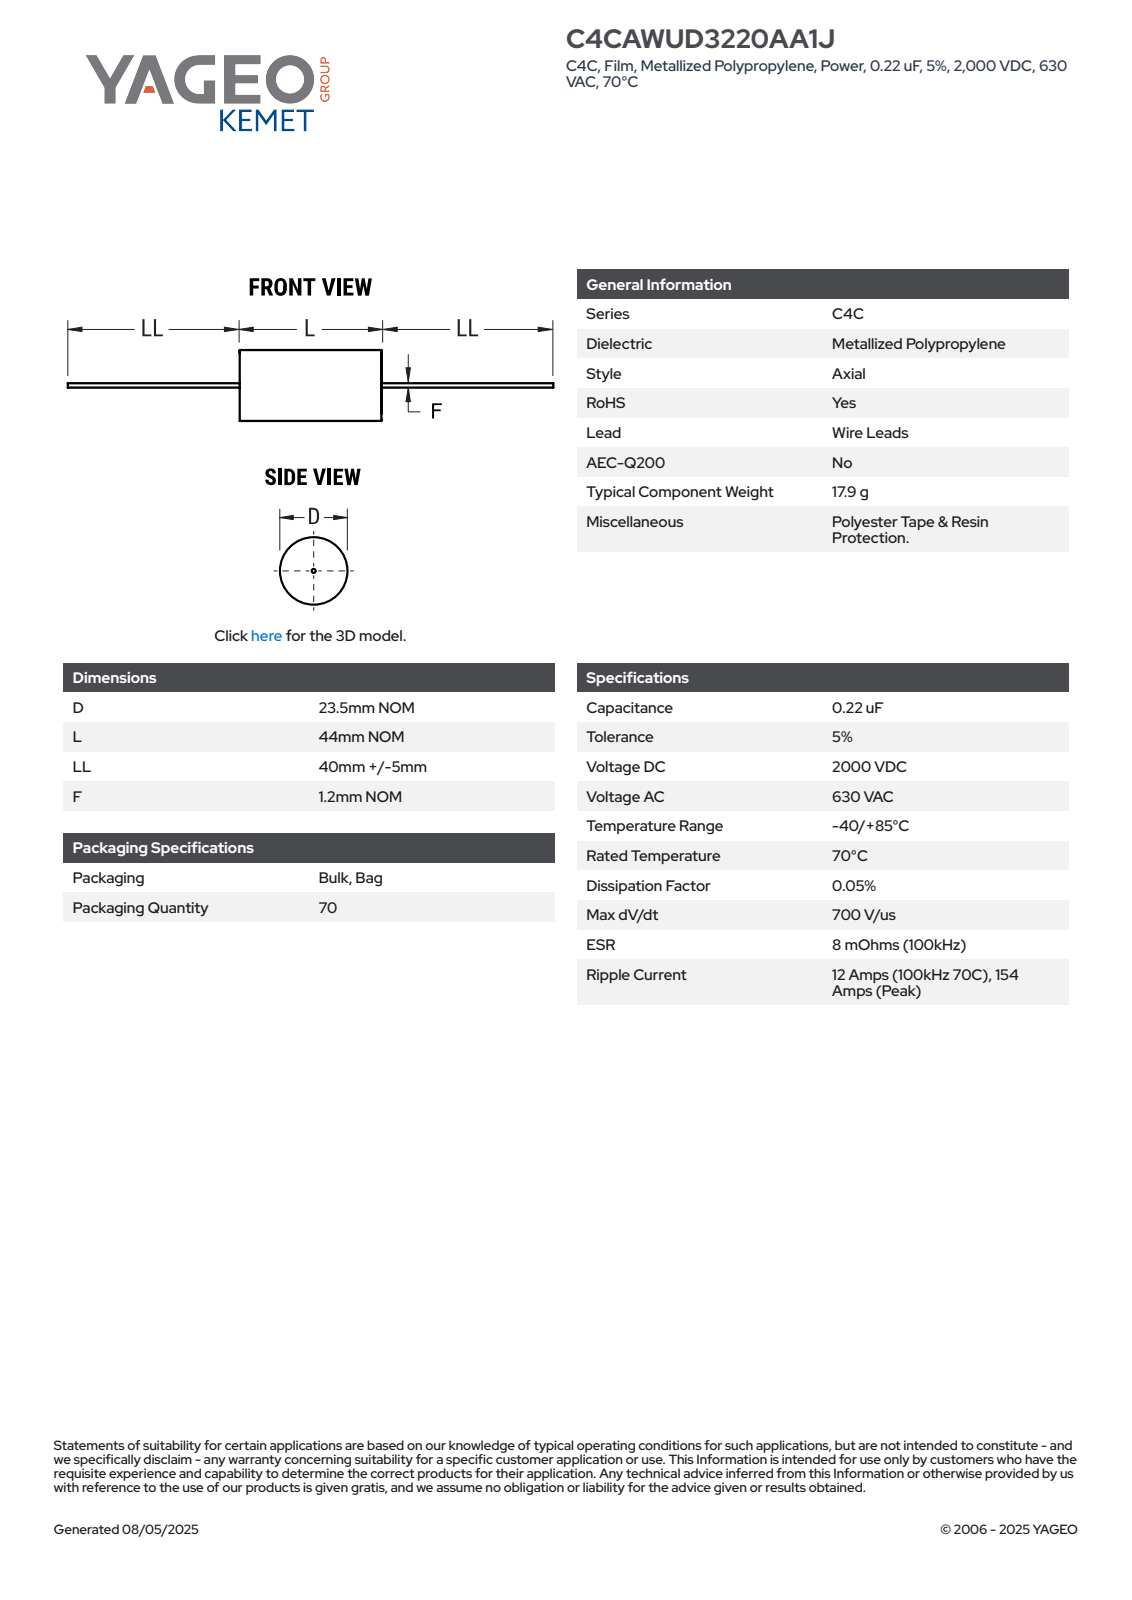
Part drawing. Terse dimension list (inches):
name: CFP_ACWF_23.5X44_D23.5L44LL45F1.2
written by: SolidWorks 2014 (AUTOMOTIVE_DESIGN)
unit: in
bodies: 2 solids, 87 faces (28 planar, 28 cylindrical, 31 other)
size: 5.276 × 0.925 × 0.925
volume: 1.171 in³; area: 8.248 in²
bosses: 1× ⌀0.925, 1× ⌀0.047
rounds: 1× R0.462
face distances: 1.732, 1.732, 1.771, 1.772, 3.504, 5.276, 3.504, 3.504, 1.772
